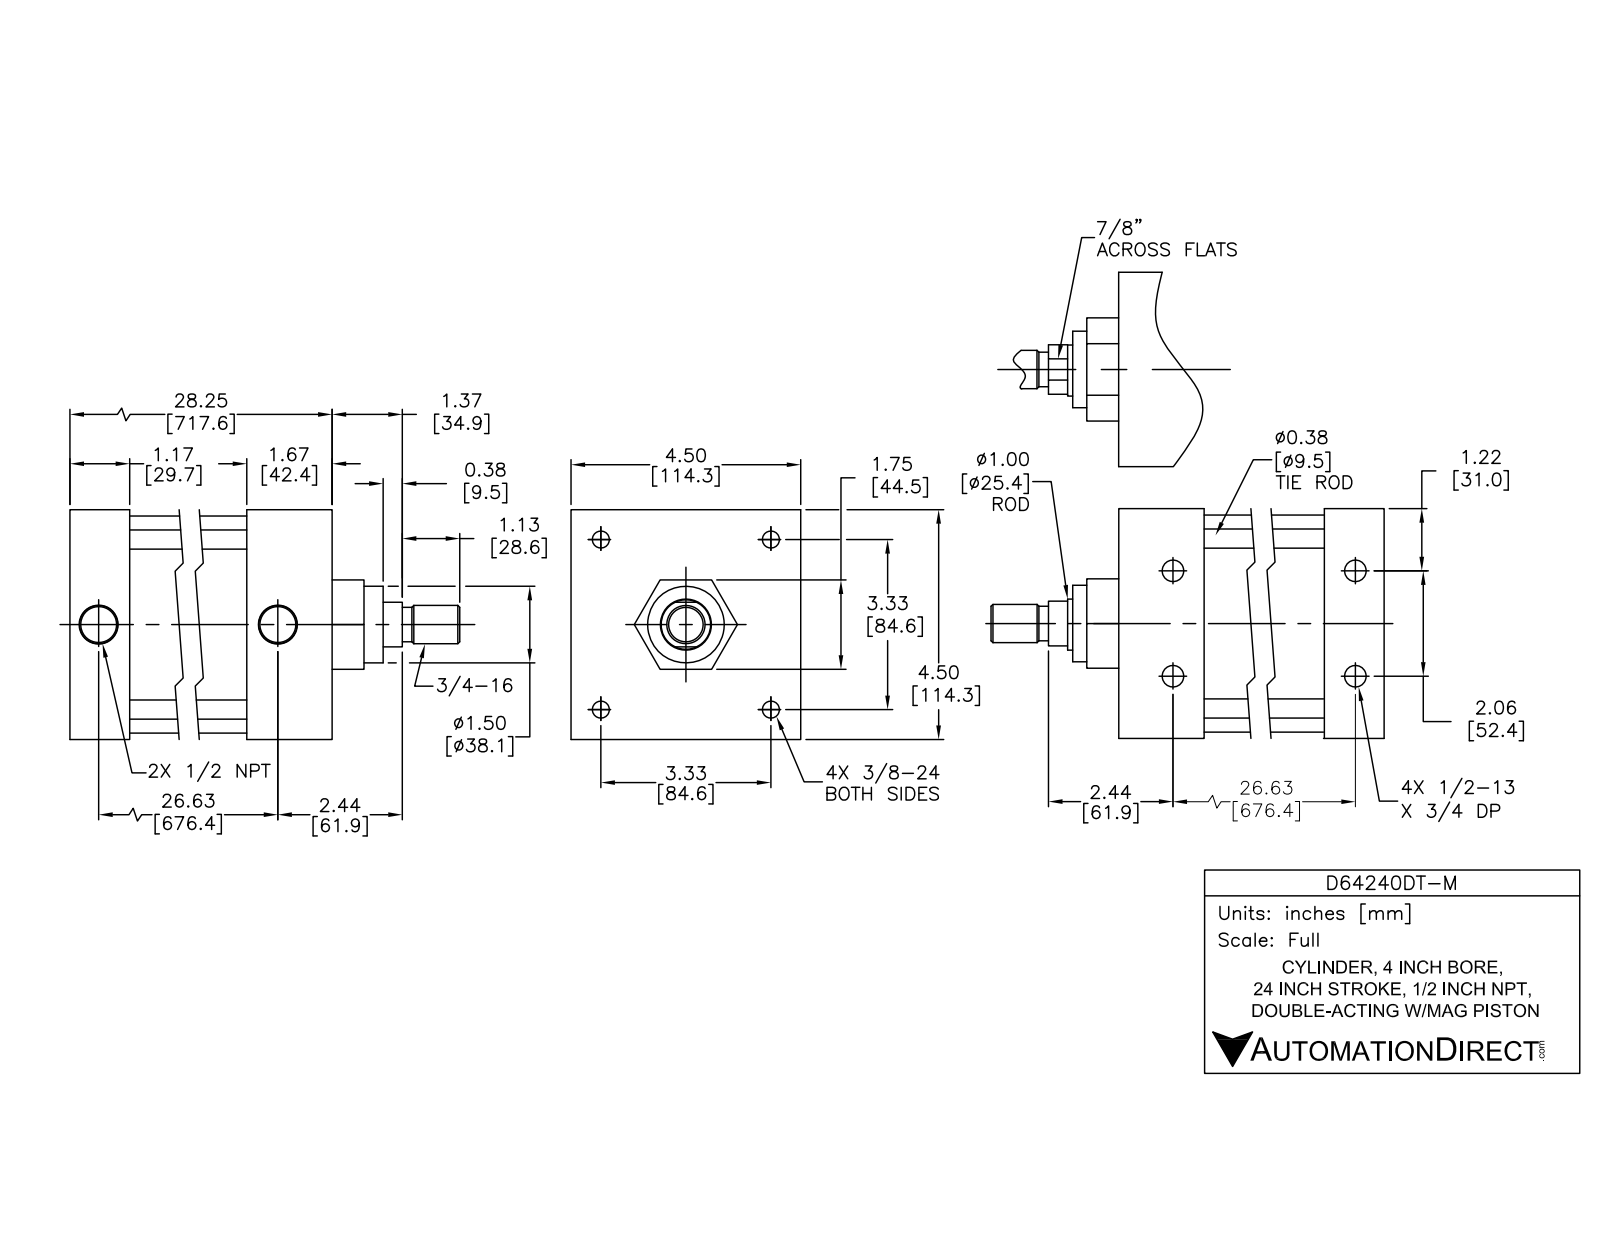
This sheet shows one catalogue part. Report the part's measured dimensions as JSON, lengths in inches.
{"part_name": "D64240DT-M PISTON; D64240DT-M BODY; D64240DT-M", "step_written_by": "SolidWorks 2015 (AUTOMOTIVE_DESIGN)", "units": "inches", "bodies": {"solids": 12, "faces": 303, "planar": 99, "cylindrical": 114, "other": 90}, "overall_size": [30.745, 4.5, 4.5], "volume_in3": 143.7, "surface_area_in2": 1090, "round_holes": [[0.33, 4], [0.406, 4], [0.417, 4], [0.625, 4], [0.5, 2], [0.766, 2], [1, 1], [1.003, 1], [4, 1]], "round_bosses_or_shafts": [[0.609, 4], [0.375, 4], [0.34, 4], [4.25, 1], [3.997, 1], [1.75, 1], [0.997, 1], [0.97, 1]], "partial_cylinders_radius": [[0.45, 4]], "face_to_face_distances": [4.5, 0.08, 25.326, 28.246, 1.75, 26.997, 1.249, 25.751, 1.246, 2.495], "hole_center_spacings": [2.349, 3.322, 26.642, 26.622, 1.031, 1.031, 2.062, 4.698]}
